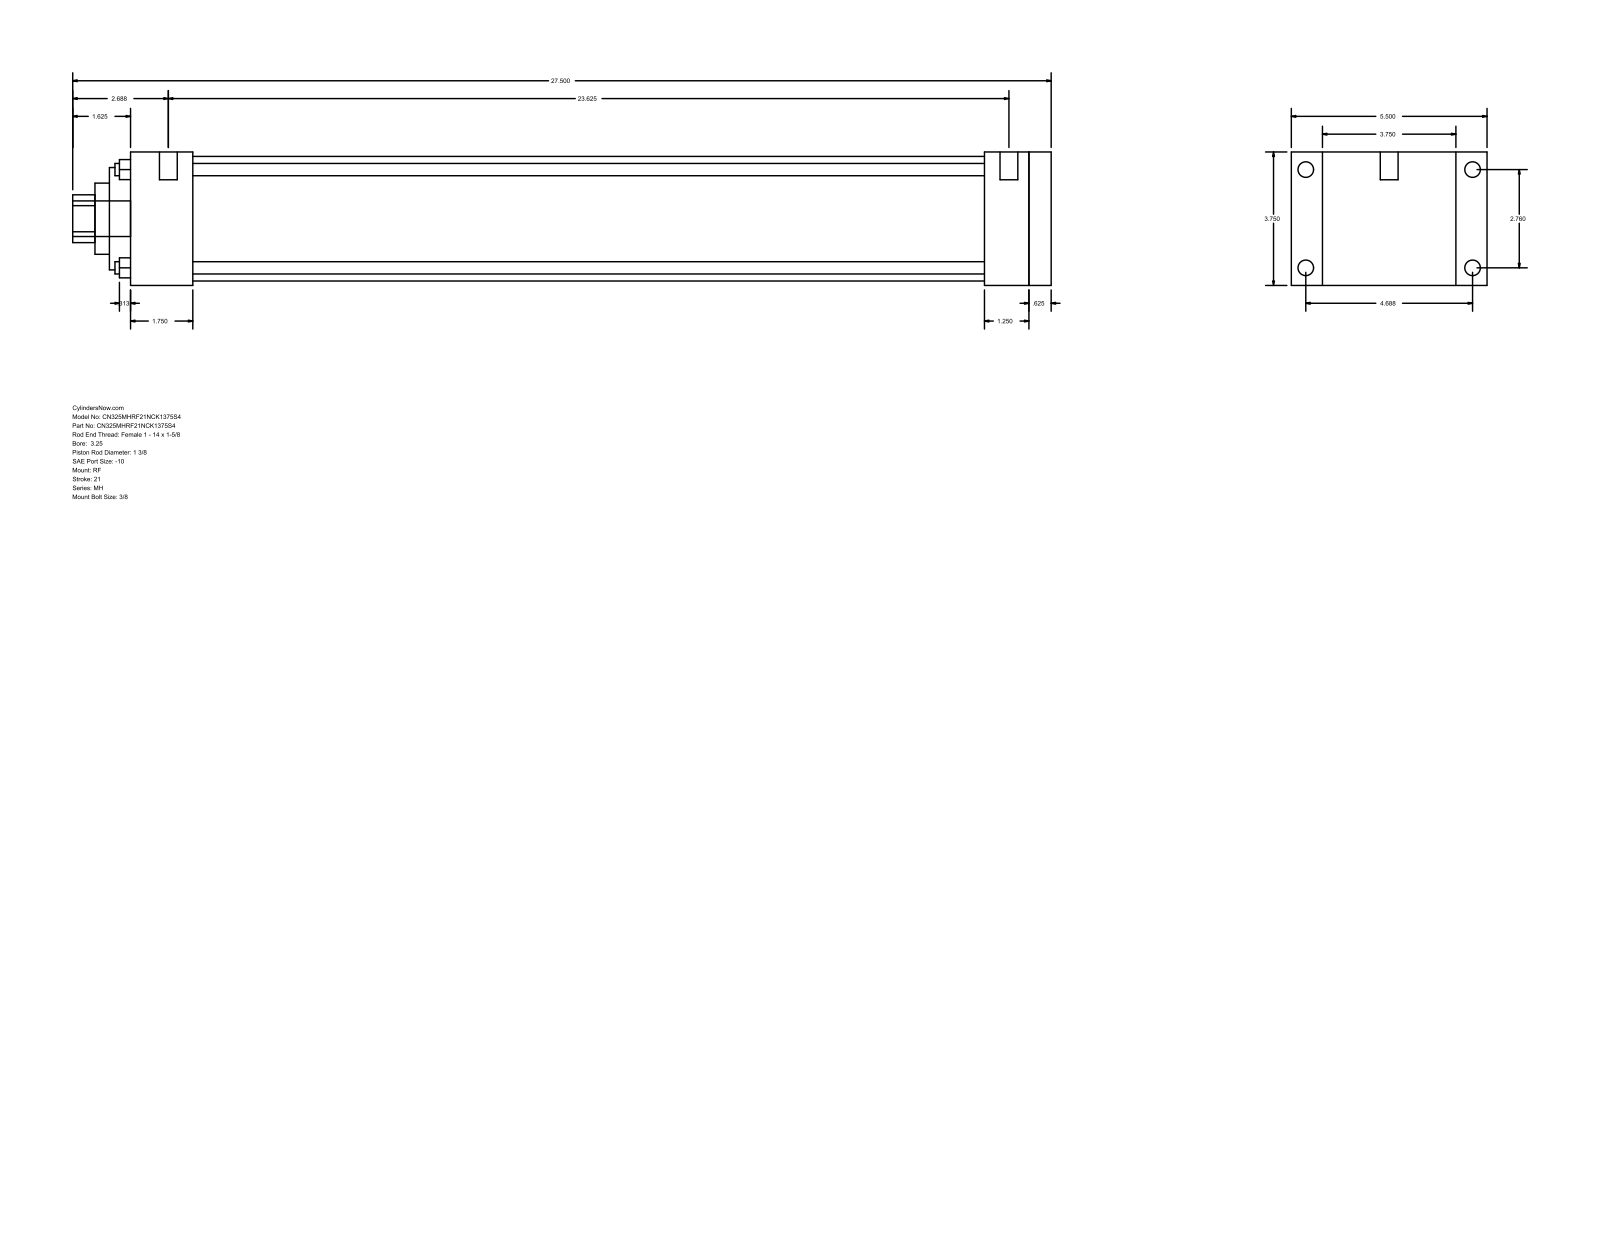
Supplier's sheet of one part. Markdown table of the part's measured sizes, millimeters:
| quantity | value |
| --- | --- |
| part name | MH_RF__0325_1.375 |
| STEP written by | GSSL Pune (CONFIG_CONTROL_DESIGN) |
| units | millimeters |
| bodies | 0 solids, 94 faces (65 planar, 29 cylindrical, 0 other) |
| overall size | 698.5 × 139.7 × 95.25 |
| round holes (diameter × count) | 8.76 × 4, 34.92 × 1, 50.8 × 1, 73.03 × 1, 88.9 × 1 |
| round bosses / shafts (diameter × count) | 11.13 × 4, 5.56 × 4, 12.7 × 2, 25.4 × 1 |
| partial cylindrical surfaces (radius × count) | 17.06 × 1 |
| main face-to-face distances | 95.24, 657.23, 15.88, 641.35, 22.23, 117.47, 44.45, 596.9, 612.78, 609.61 |
| hole center spacings | 49.57, 70.1, 99.14 |
